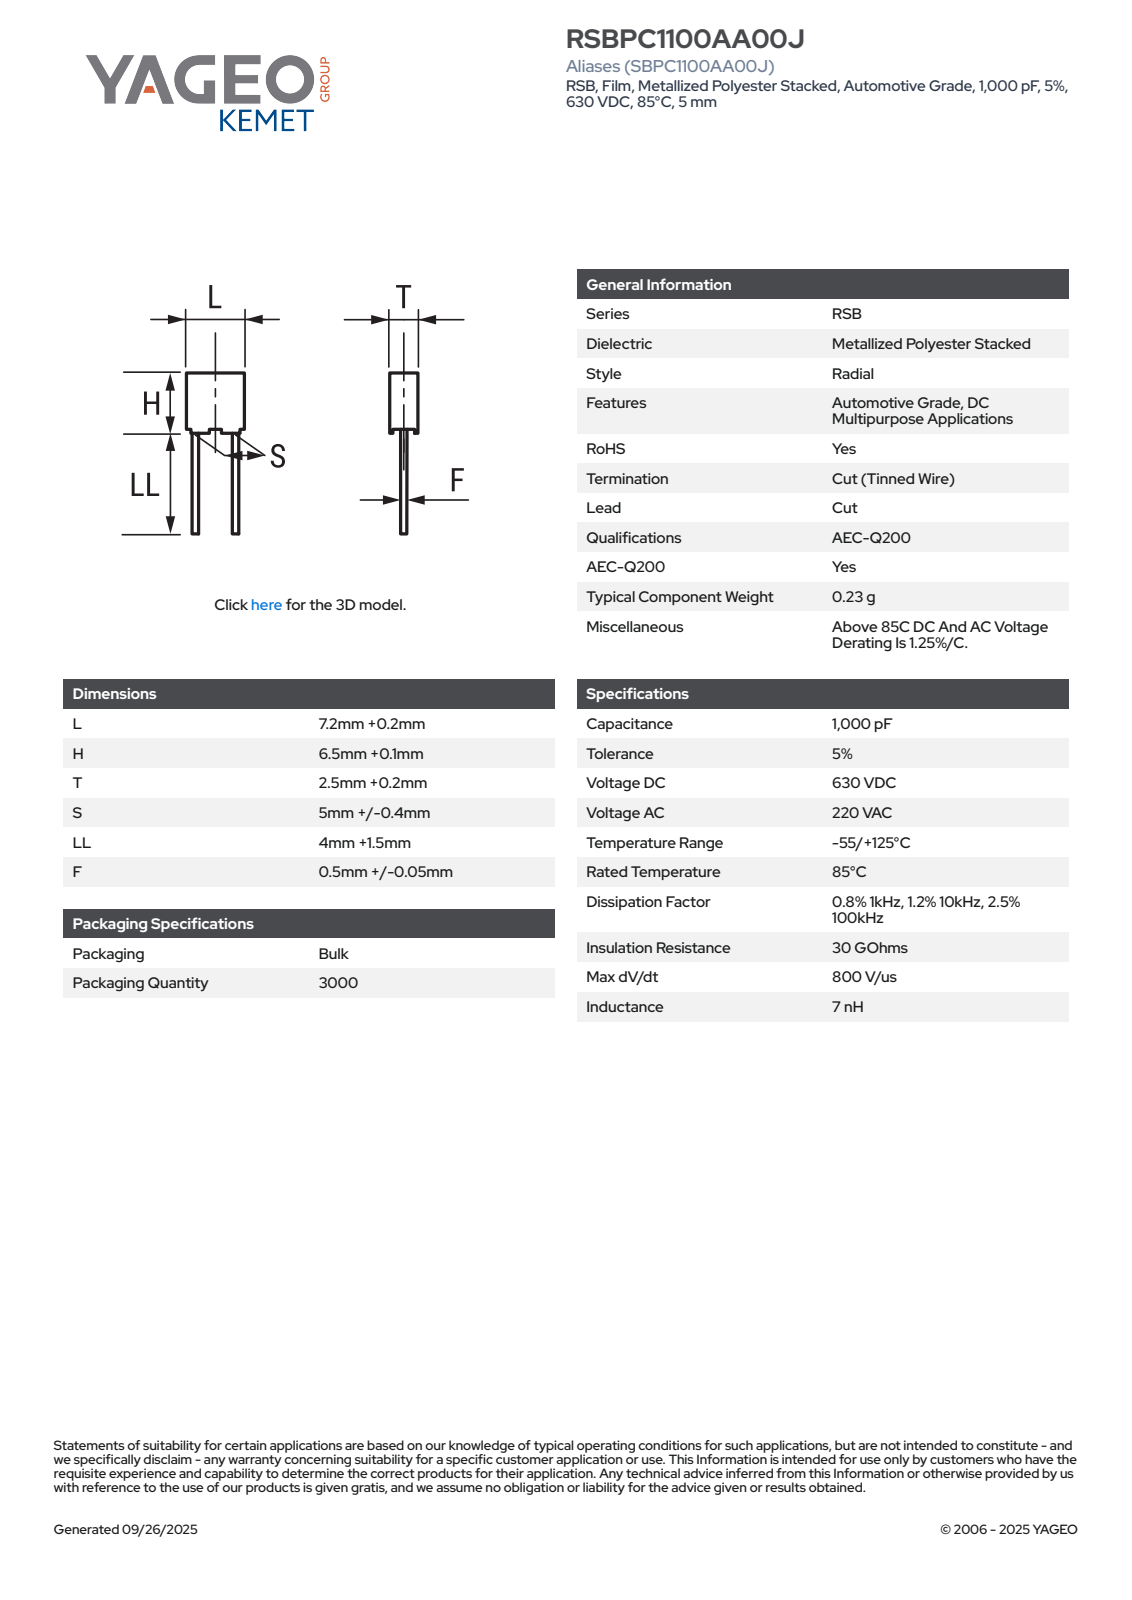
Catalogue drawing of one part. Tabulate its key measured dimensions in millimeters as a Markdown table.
| quantity | value |
| --- | --- |
| part name | CFR_RB3_7.2X6.5X2.5_L7.4H6.6T2.7S5LL5.5F0.65 |
| STEP written by | SolidWorks 2014 (AUTOMOTIVE_DESIGN) |
| units | millimeters |
| bodies | 4 solids, 85 faces (77 planar, 8 cylindrical, 0 other) |
| overall size | 12.1 × 7.4 × 2.71 |
| volume | 123 mm³ |
| surface area | 211 mm² |
| round bosses / shafts (diameter × count) | 0.65 × 2 |
| partial cylindrical surfaces (radius × count) | 0.5 × 4 |
| main face-to-face distances | 2.7, 7.4, 5.85, 2.45, 2.2, 0.75, 6.6, 7.15, 6.9, 2.46 |
